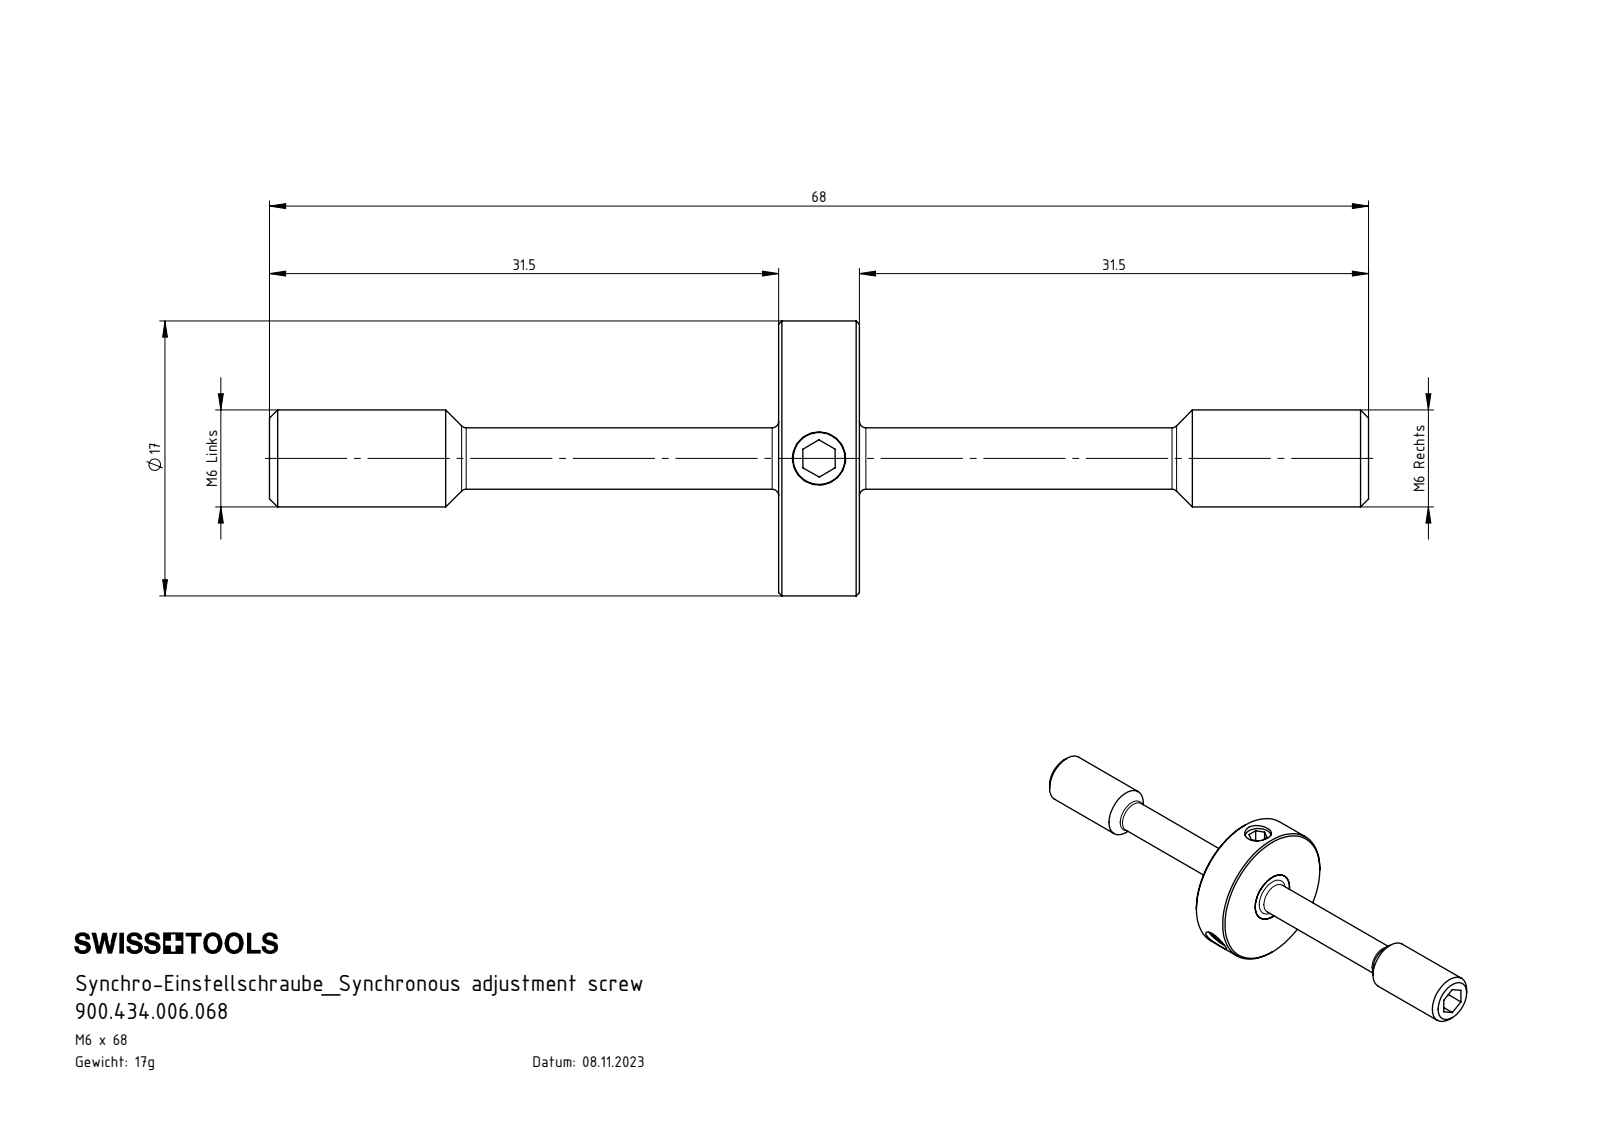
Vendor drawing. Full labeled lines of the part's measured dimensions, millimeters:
Part name (STEP PRODUCT): 900.434.006.068; Z72-ER3.001.068_A; Z42-ER3.002.005_A; ISO 4026 - M4 x 5
STEP written by: SolidWorks 2022 (AUTOMOTIVE_DESIGN)
Units: millimetres
Bodies: 5 solids, 99 faces (39 planar, 26 cylindrical, 34 other)
Overall size (bounding box): 68 × 17 × 17
Volume: 2 213 mm³ · Surface area: 2 285 mm²
Round holes (diameter × count): ⌀3.3 ×3
Round bosses / shafts (diameter × count): ⌀4 ×3, ⌀17 ×1, ⌀6 ×1, ⌀3.8 ×1
Main face-to-face distances: 5, 31.5, 36.5, 2, 2.5, 3, 68, 33, 35, 1.5
